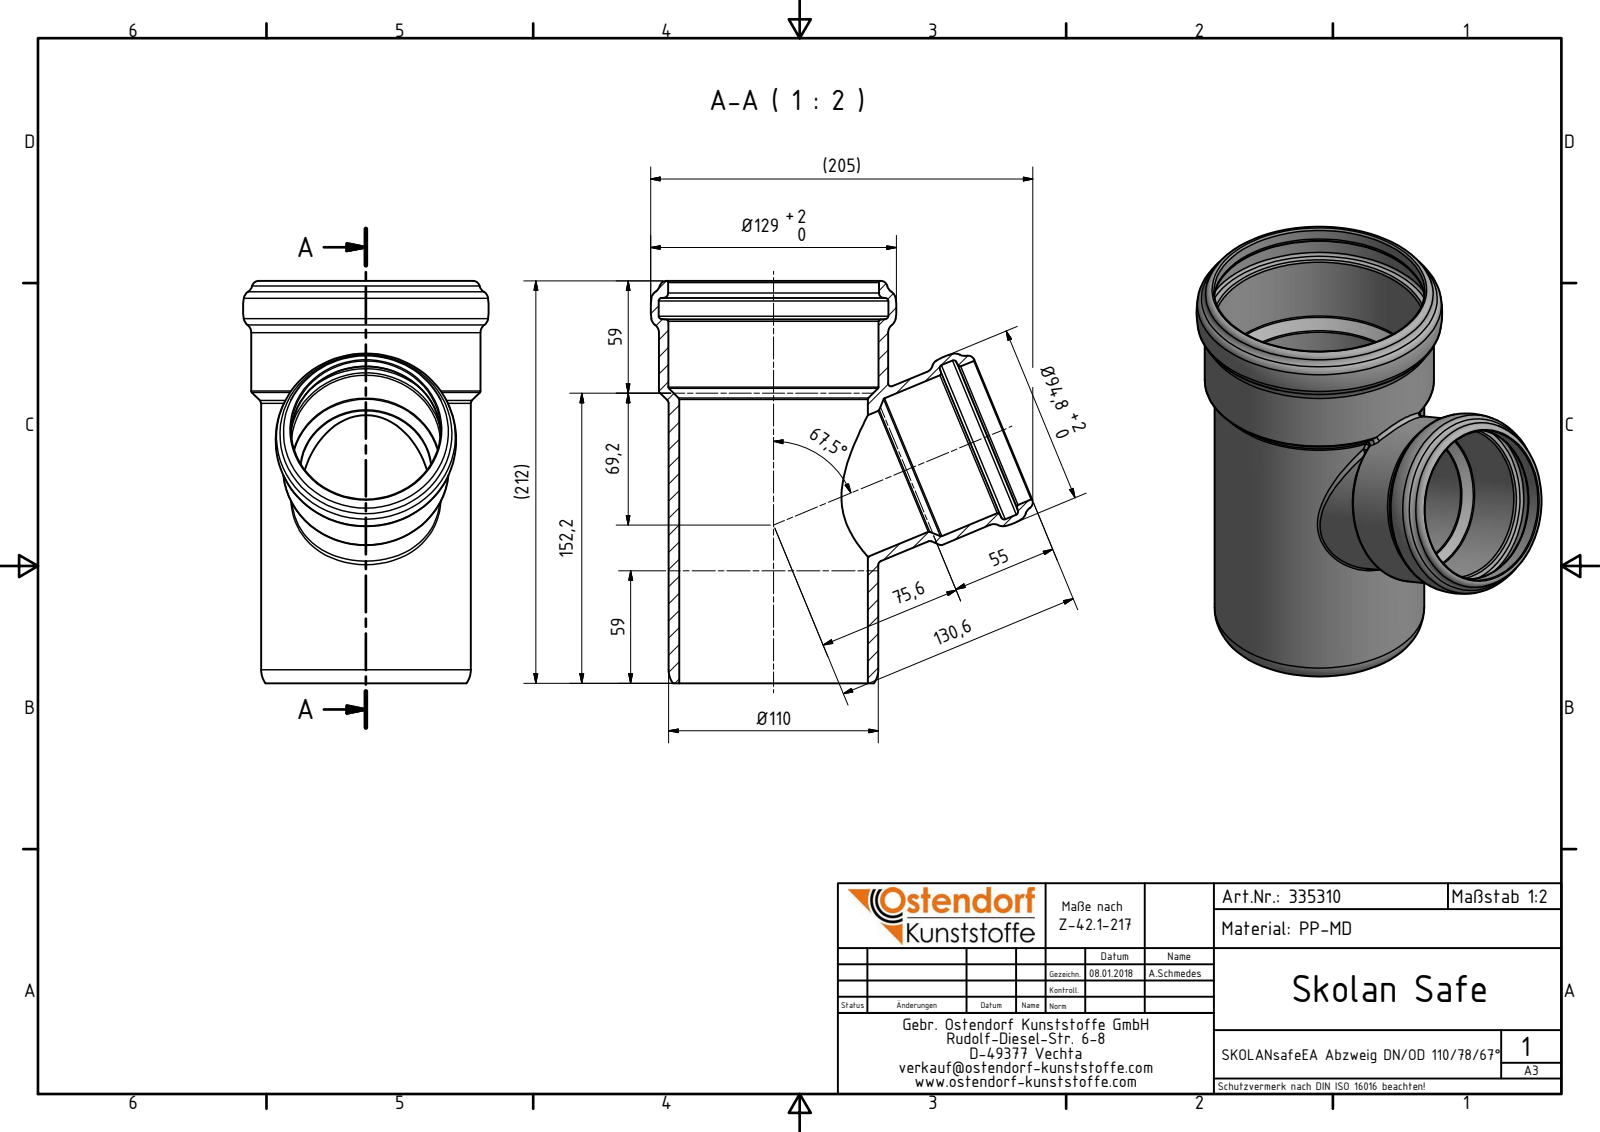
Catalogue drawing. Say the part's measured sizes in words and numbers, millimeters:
The part is named "335310 SKOLANsafeEA Abzweiger DN_OD 110_78_67°". Its 3-D file was written by "Autodesk Inventor 2016 (AUTOMOTIVE_DESIGN)". It is 1 solid with 70 faces: 1 planar, 12 cylindrical and 57 other. Overall it measures 211.2 by 200.68 by 129 millimeters. Its volume is 456 565 cubic millimeters and its surface area 185 470 square millimeters. Round holes: 1 of diameter 68.7, 1 of diameter 78.4, 1 of diameter 78.7, 1 of diameter 87.6, 1 of diameter 99.1, 1 of diameter 110.4, 1 of diameter 110.7, 1 of diameter 120.6. Round bosses or shafts: 1 of diameter 120.4, 1 of diameter 110.1, 1 of diameter 87, 1 of diameter 78.1.
